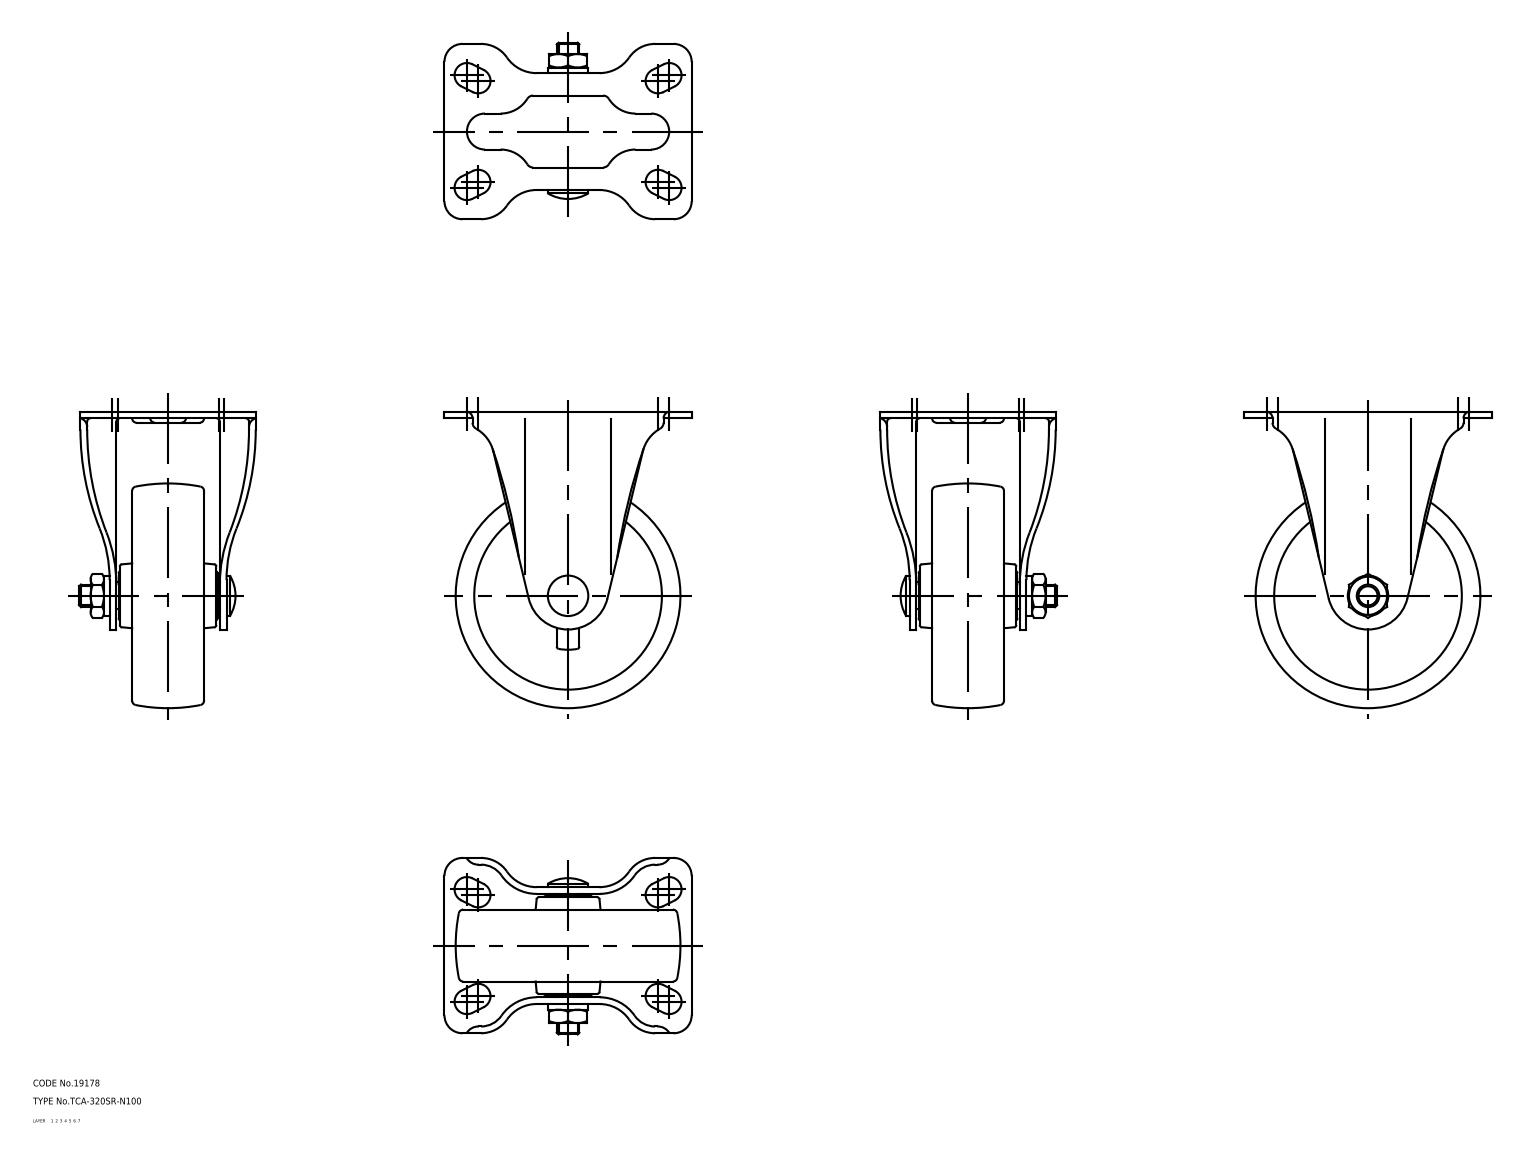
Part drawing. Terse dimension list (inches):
name: 67123922; 67123935; 67123948; 67123961 (+2 more)
written by: CADfix (AUTOMOTIVE_DESIGN)
unit: in
bodies: 3 solids, 251 faces (0 planar, 0 cylindrical, 251 other)
size: 5.197 × 4.331 × 3.091
volume: 14.03 in³; area: 110 in²
